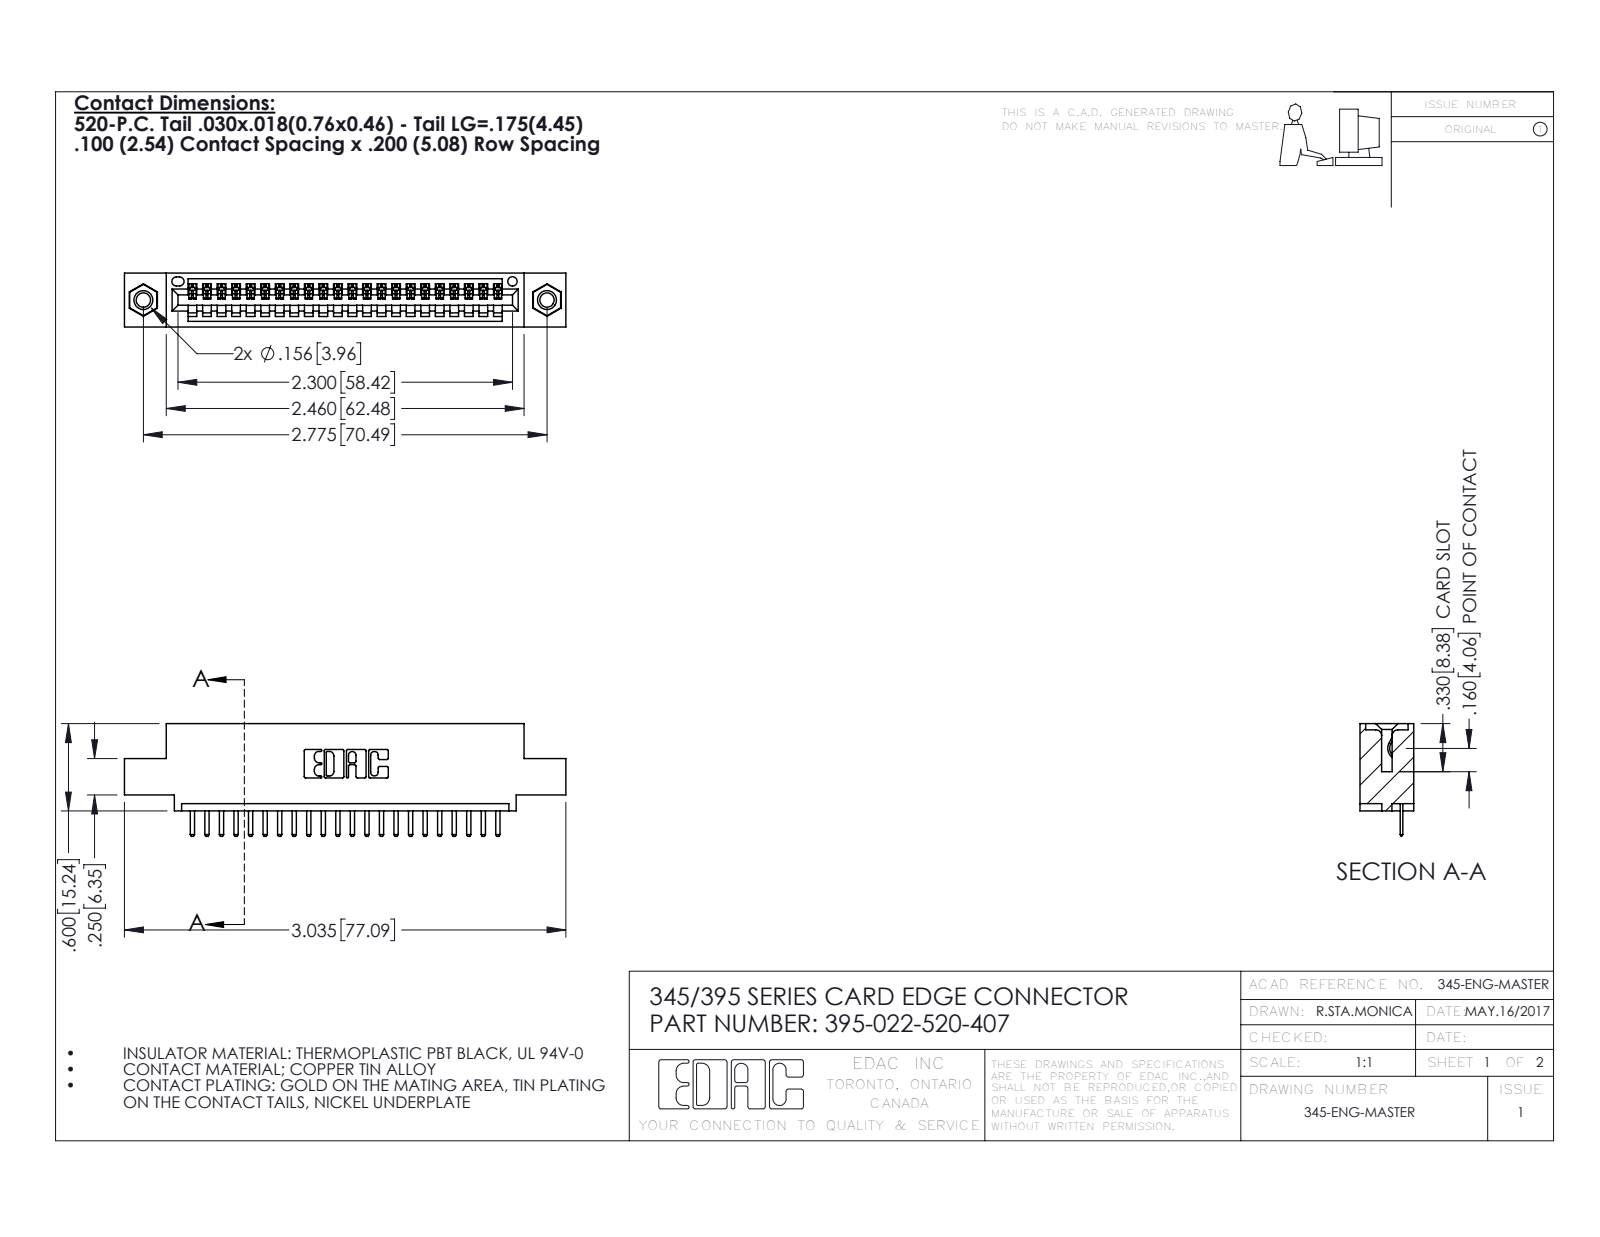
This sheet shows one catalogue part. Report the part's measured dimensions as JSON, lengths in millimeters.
{"part_name": "345 Part_0.110 Offset - 0.156 Dia-TI; 395-022-520-407; 345-250-001_345-250-005-103; 345-292-001_345-293-120", "step_written_by": "SolidWorks 2016 (CONFIG_CONTROL_DESIGN)", "units": "millimeters", "bodies": {"solids": 25, "faces": 1554, "planar": 1040, "cylindrical": 498, "other": 16}, "overall_size": [77.1, 19.7, 9.4], "volume_mm3": 7010, "surface_area_mm2": 8948, "round_holes": [[2.5, 2], [3.2, 2], [4, 2], [1.6, 1]], "round_bosses_or_shafts": [[3.9, 2]], "partial_cylinders_radius": [[0.3, 46], [0.2, 44], [0.3, 22], [0.2, 6], [0.8, 6], [0.7, 3], [0.8, 2], [1, 2]], "face_to_face_distances": [1.8, 7.6, 9.4, 5.1, 2.5, 6.9, 0.6, 5.7, 1.8, 3.8], "hole_center_spacings": [6.9, 64.5, 70.5]}
